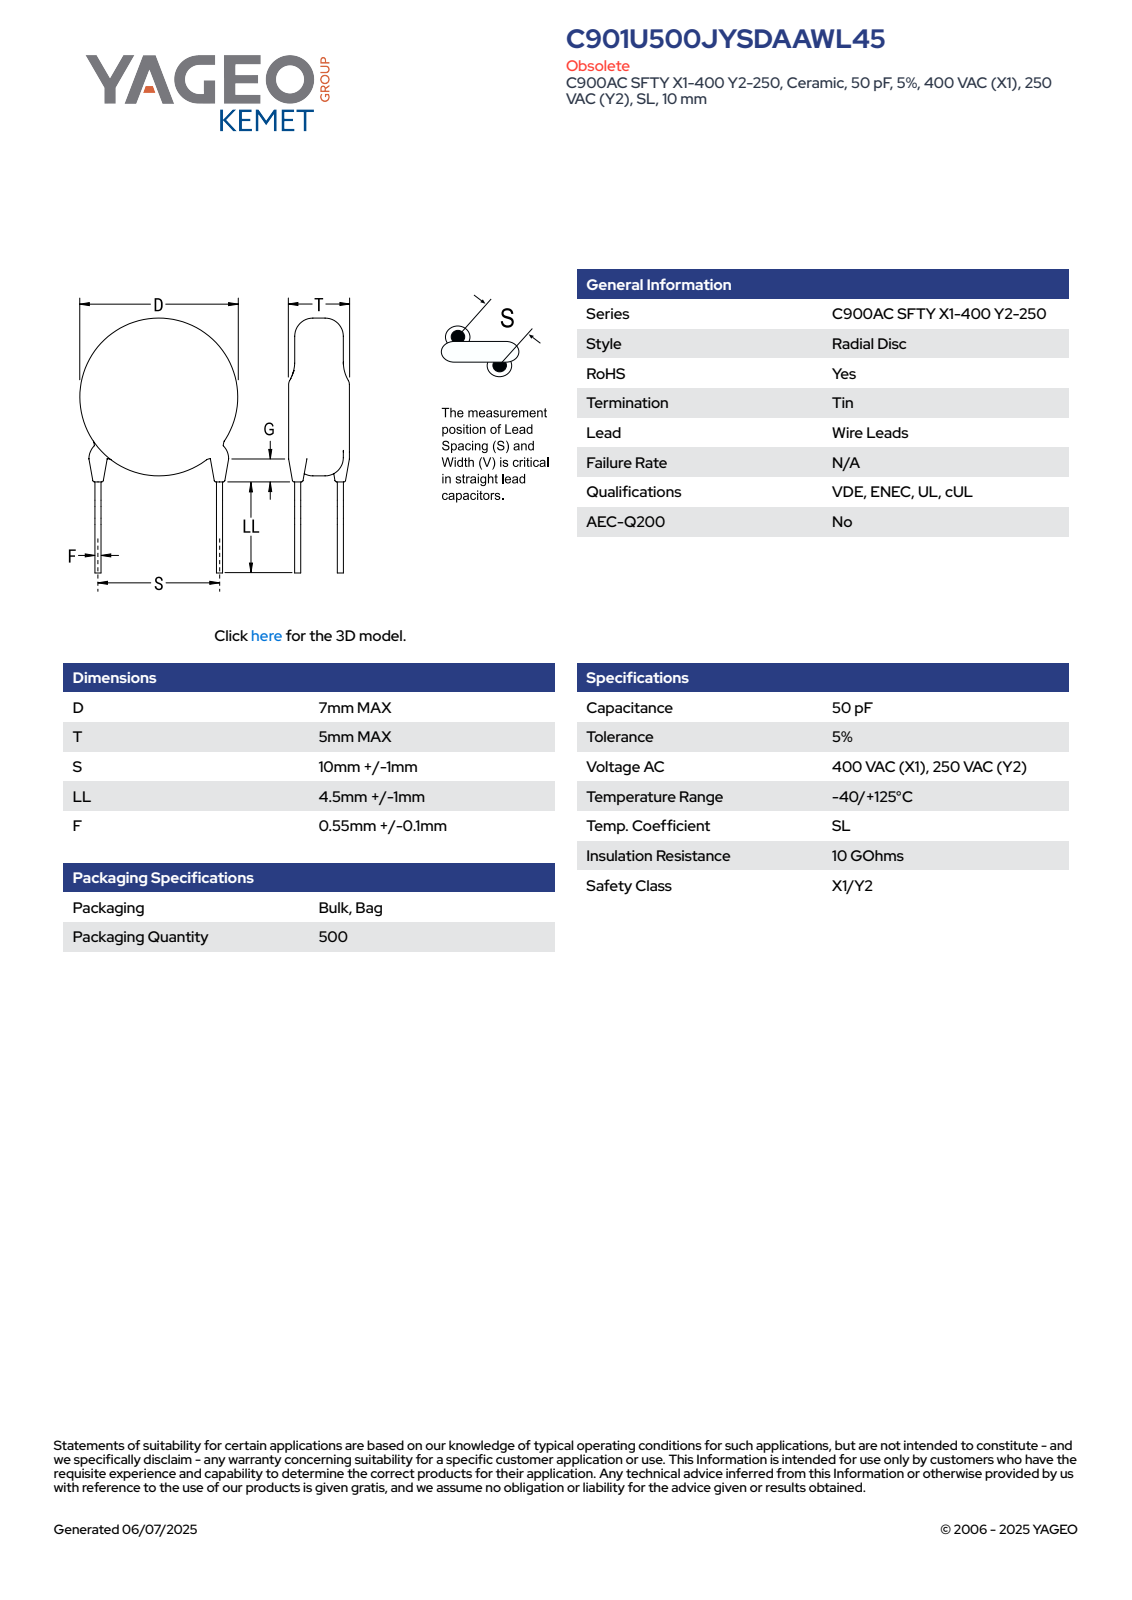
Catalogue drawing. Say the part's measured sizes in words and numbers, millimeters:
The part is named "CCD_STC900_D7T5S10LL5.5F0.65G3". Its 3-D file was written by "SolidWorks 2014 (AUTOMOTIVE_DESIGN)". It is 4 solids with 83 faces: 61 planar, 6 cylindrical and 16 other. Overall it measures 12.96 by 10.02 by 5 millimeters. Its volume is 193 cubic millimeters and its surface area 211 square millimeters. Round bosses or shafts: 2 of diameter 0.65, 1 of diameter 7. The main face-to-face distances are 5, 0.81, 9.85, 9.04, 3.3, 1.67, 3.52, 2.4, 2.49, 1.32.
